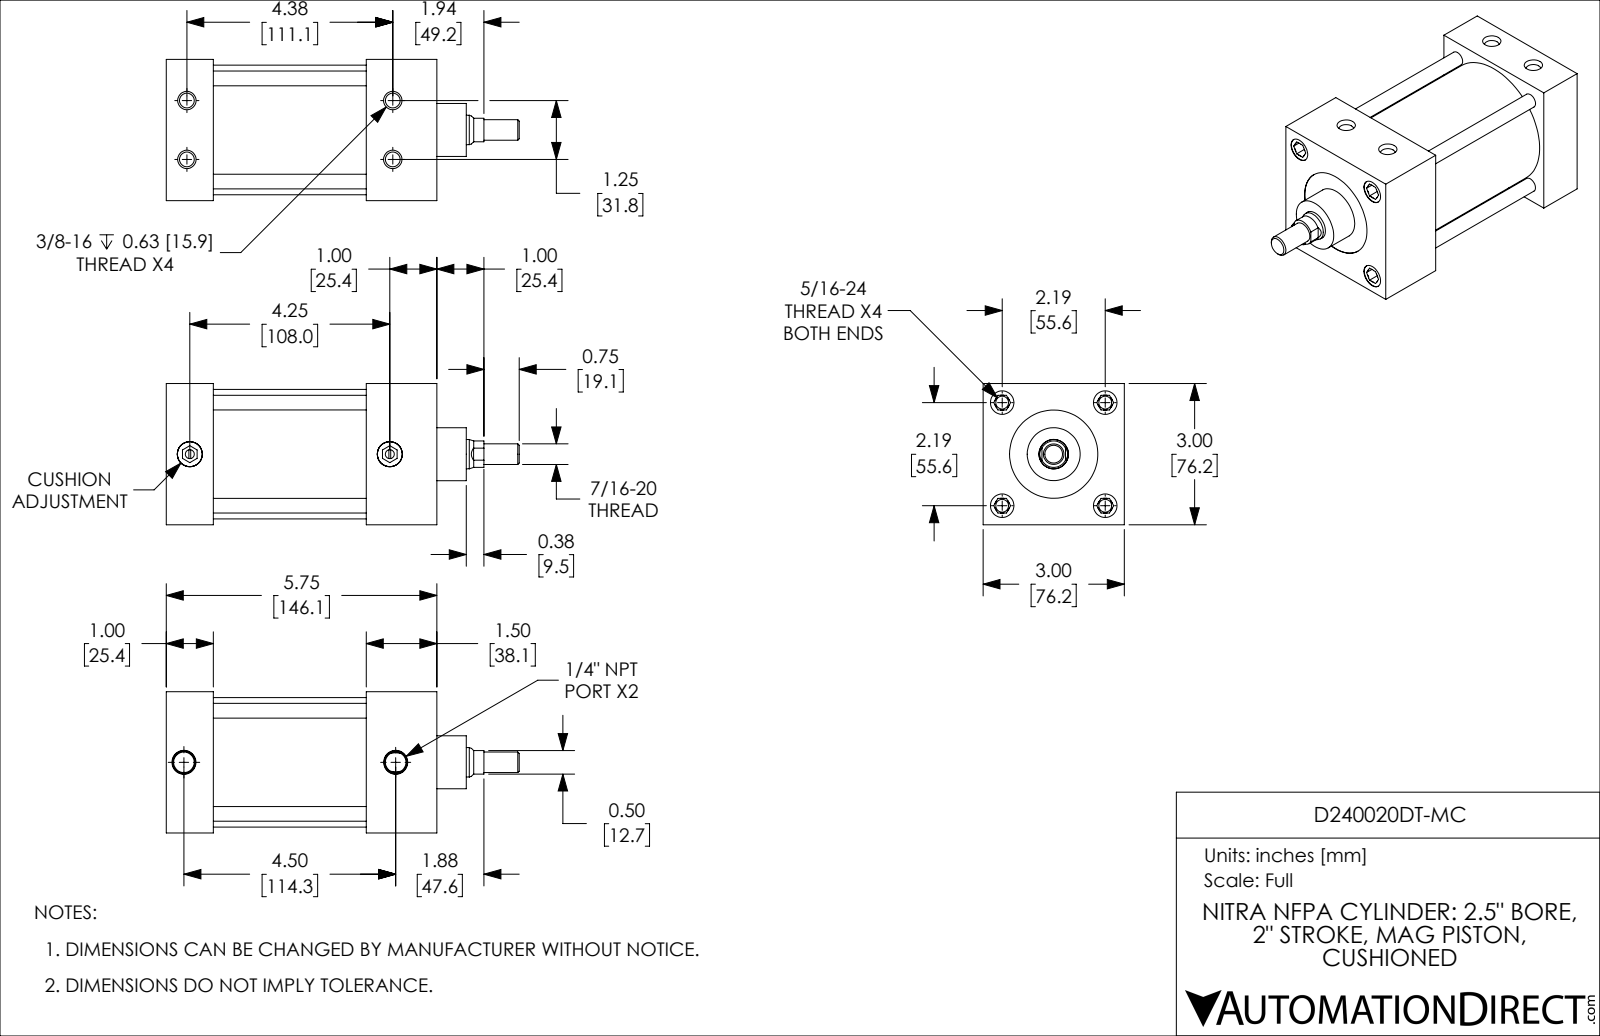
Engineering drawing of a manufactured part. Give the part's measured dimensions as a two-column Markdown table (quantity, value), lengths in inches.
| quantity | value |
| --- | --- |
| part name | D240020DT-MC_CUSHION; D240020DT-MC_PISTON_KK1; D240020DT-MC_BODY; D240020DT-MC |
| STEP written by | SolidWorks 2019 (CONFIG_CONTROL_DESIGN) |
| units | inches |
| bodies | 4 solids, 248 faces (90 planar, 78 cylindrical, 80 other) |
| overall size | 7.5 × 3 × 3 |
| volume | 33.29 in³ |
| surface area | 179 in² |
| round holes (diameter × count) | 0.272 × 4, 0.313 × 4, 0.5 × 4, 0.19 × 2, 0.438 × 2, 0.531 × 2, 0.626 × 1, 1.875 × 1, 2.501 × 1 |
| round bosses / shafts (diameter × count) | 0.312 × 4, 0.532 × 2, 2.751 × 1, 2.499 × 1, 1.125 × 1, 0.624 × 1, 0.437 × 1 |
| partial cylindrical surfaces (radius × count) | 0.281 × 1 |
| main face-to-face distances | 3, 1, 3.25, 4.25, 5.75, 4.75, 1.5, 1.25, 2.25, 2 |
| hole center spacings | 1.548, 2.19, 4.481, 0.628, 0.628, 1.25, 3.097, 4.375 |
